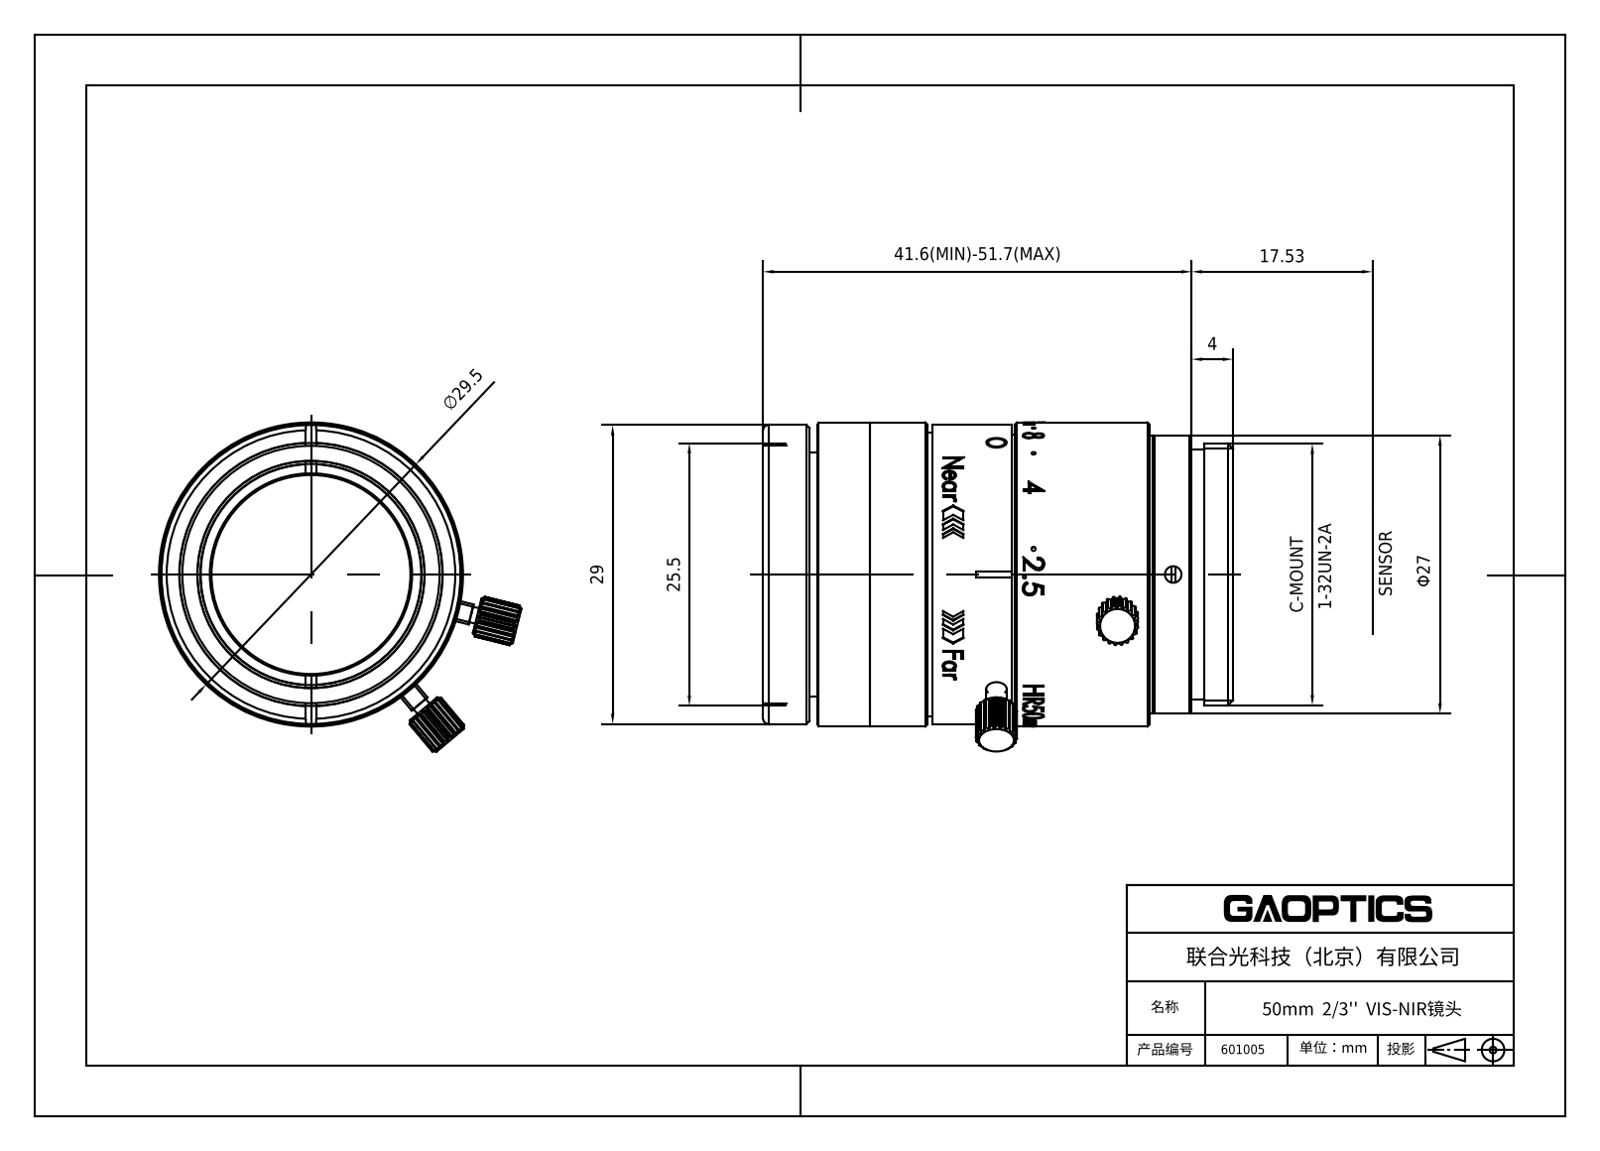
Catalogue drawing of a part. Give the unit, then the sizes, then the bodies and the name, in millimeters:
Units: millimetres
Overall size (bounding box): 45.33 × 34.5 × 29.5
Volume: 24 689 mm³ · Surface area: 9 247 mm²
Bodies: 2 solids, 614 faces (0 planar, 0 cylindrical, 614 other)
Part name (STEP PRODUCT): 601005
STEP written by: SolidWorks 2019 (CONFIG_CONTROL_DESIGN)
